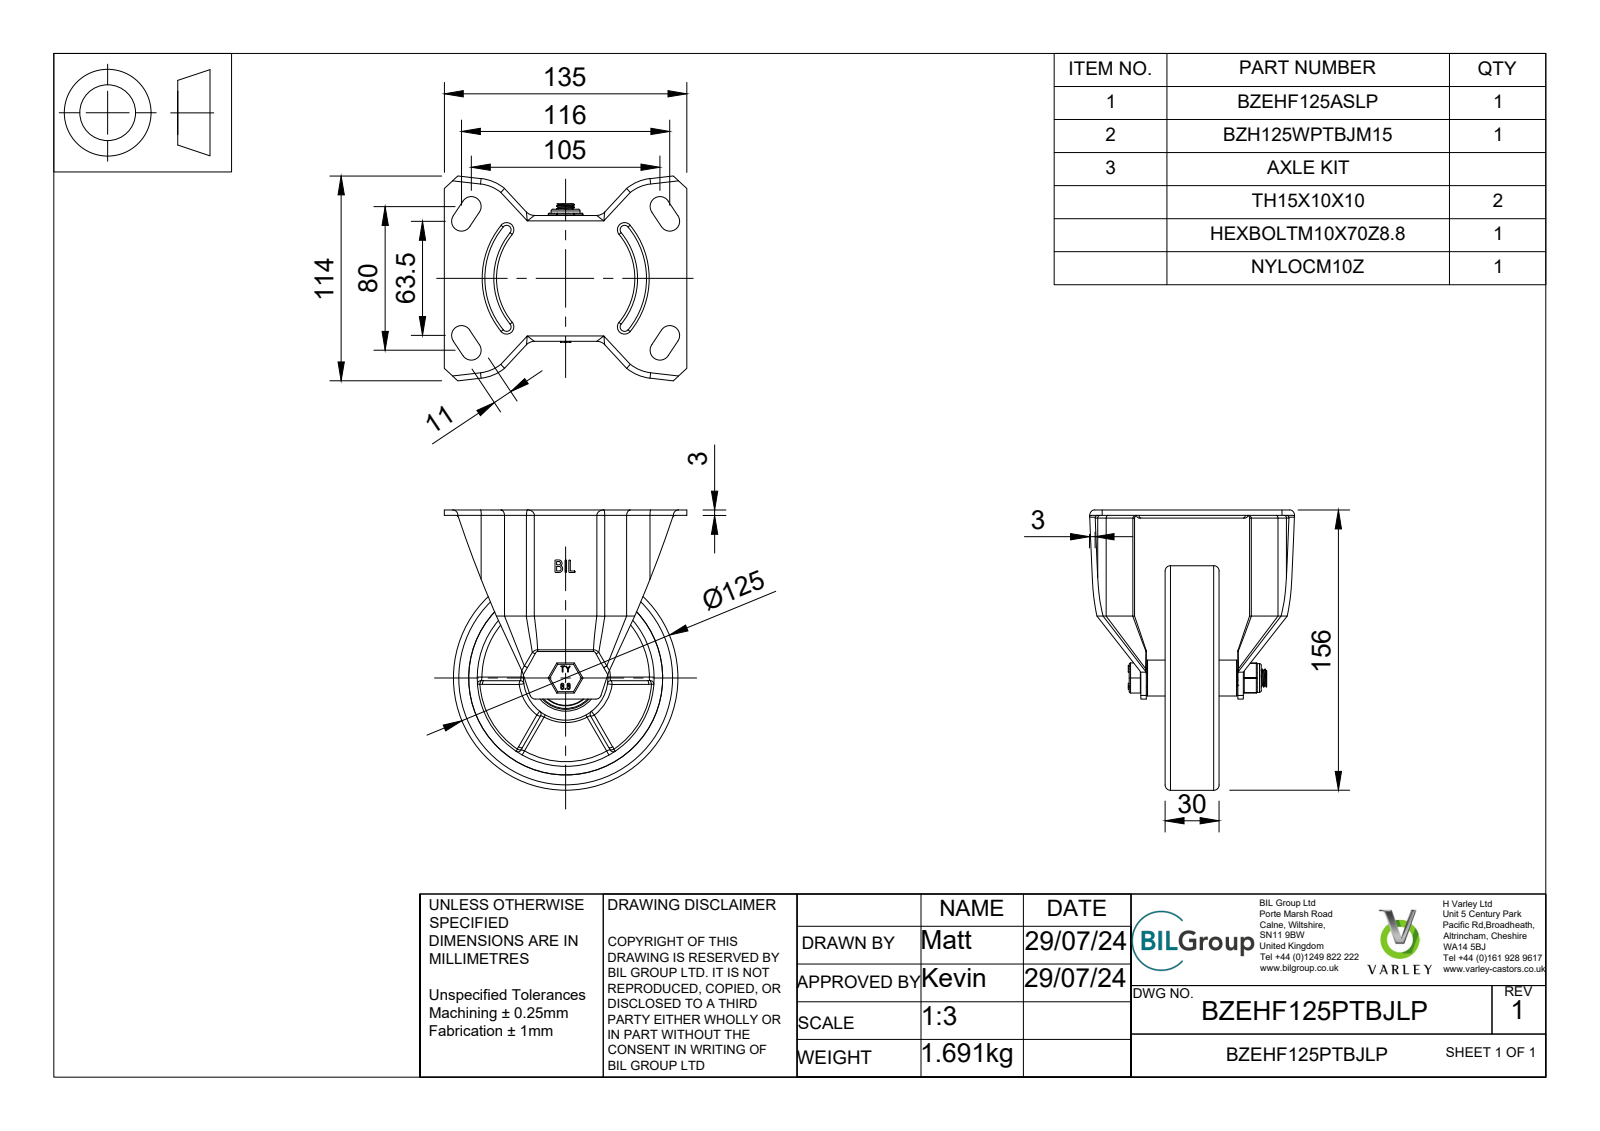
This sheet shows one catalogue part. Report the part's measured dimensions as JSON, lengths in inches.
{"part_name": "BZEHF125PTBJLP v3; BZEHF125ASLP v1; ZINC PLATED, PRESSED STEEL BRACKET; BZH125WPTBJM15 v1 (+7 more)", "step_written_by": "Autodesk Translation Framework v13.14.0.145 (AUTOMOTIVE_DESIGN)", "units": "inches", "bodies": {"solids": 35, "faces": 1287, "planar": 436, "cylindrical": 240, "other": 611}, "overall_size": [6.142, 5.315, 4.488], "volume_in3": 18.47, "surface_area_in2": 252.9, "round_holes": [[0.394, 1], [0.402, 1], [0.413, 1], [0.472, 1], [0.591, 1], [0.886, 1], [1.181, 1], [1.22, 1], [1.26, 1], [1.378, 1], [3.878, 1], [4.252, 1]], "round_bosses_or_shafts": [[4.921, 1], [1.85, 1], [1.201, 1], [0.906, 1], [0.787, 1], [0.748, 1], [0.709, 1], [0.63, 1]], "partial_cylinders_radius": [[0.02, 18], [0.118, 18], [0.059, 14], [0.079, 12], [0.217, 8], [0.03, 6], [0.236, 4], [0.869, 4]], "face_to_face_distances": [0.118, 1.181, 0.669, 1.85, 0.256, 2.382, 0.61, 0.787, 1.969, 2.638]}
